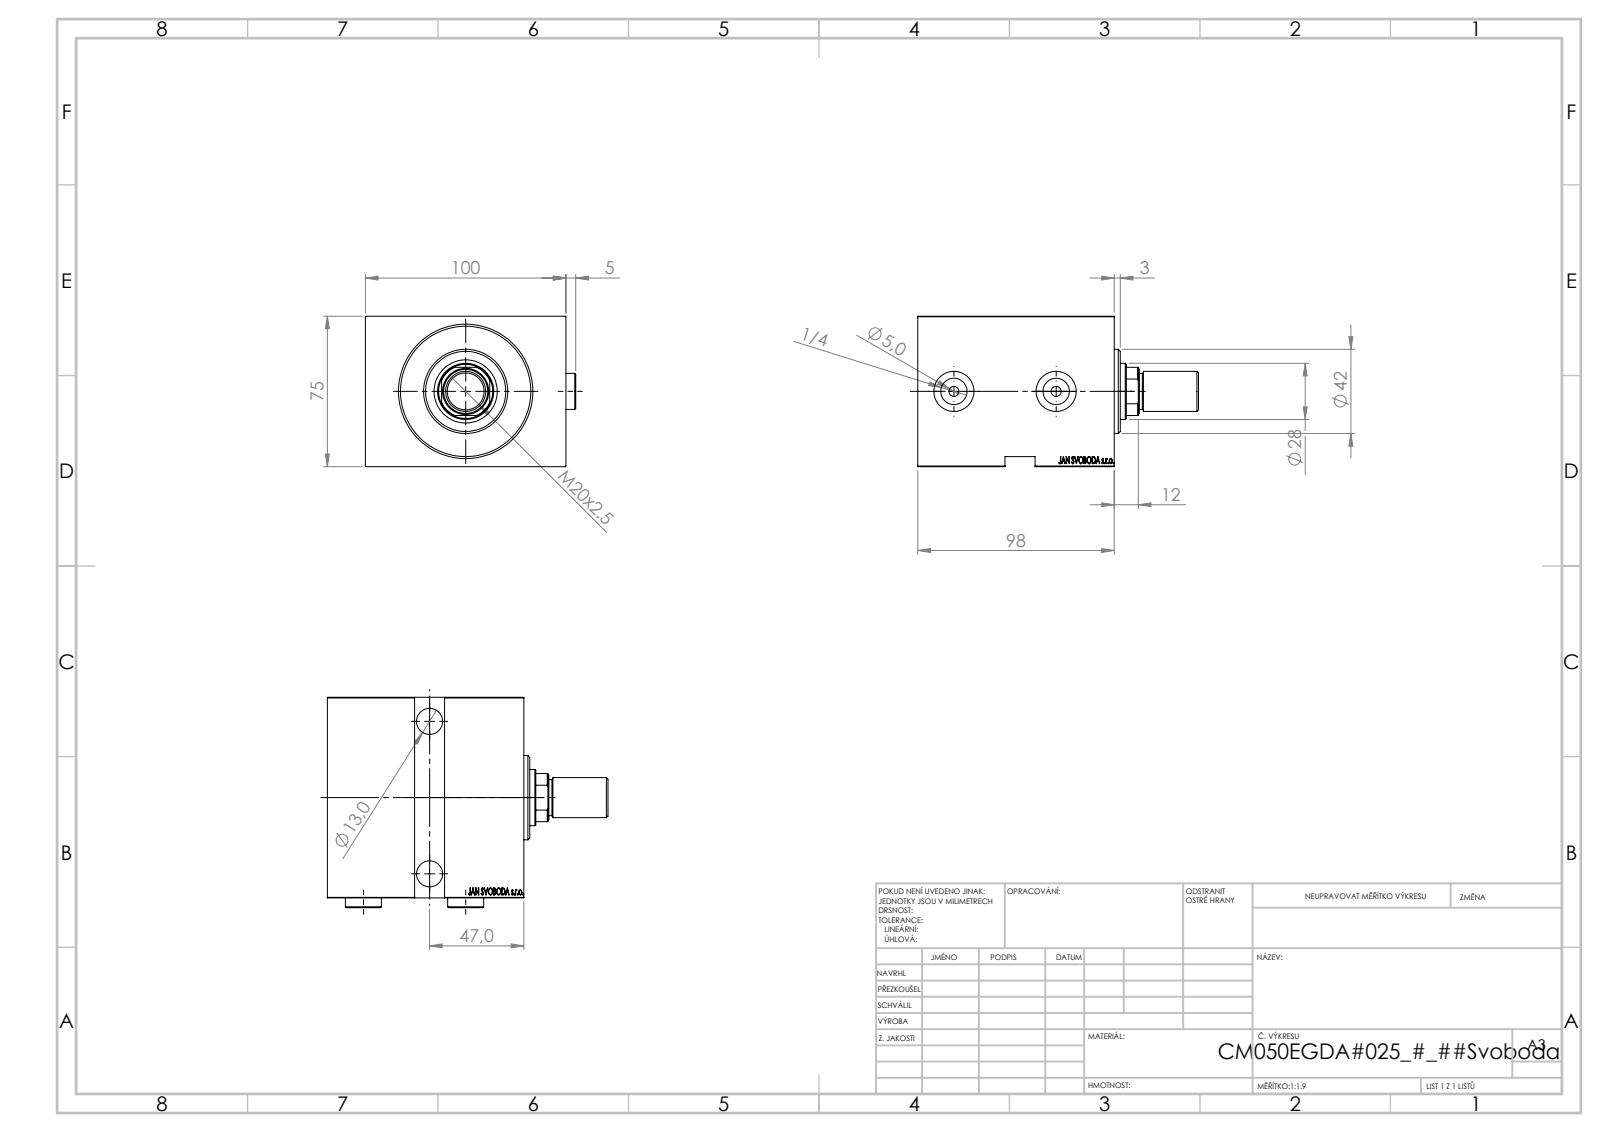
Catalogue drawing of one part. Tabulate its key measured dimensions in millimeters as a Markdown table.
| quantity | value |
| --- | --- |
| part name | V450CM_VC_B; V450CM_MALE_METRIC; V450CM_E_Body; Zatka_OIL_PORT (+1 more) |
| STEP written by | SolidWorks 2019 (CONFIG_CONTROL_DESIGN) |
| units | millimeters |
| bodies | 6 solids, 916 faces (448 planar, 64 cylindrical, 404 other) |
| overall size | 140 × 104.9 × 75 |
| volume | 681 788 mm³ |
| surface area | 104 129 mm² |
| round holes (diameter × count) | 5 × 2, 13 × 2, 13.16 × 2, 19 × 2, 20 × 2, 18.5 × 1, 28 × 1, 31.5 × 1, 50 × 1, 65 × 1 |
| round bosses / shafts (diameter × count) | 18 × 3, 52 × 1, 42 × 1, 20 × 1 |
| partial cylindrical surfaces (radius × count) | 13.5 × 1 |
| main face-to-face distances | 75, 100, 98, 5, 14, 84, 79, 93, 47, 81.4 |
| hole center spacings | 51, 76 |
